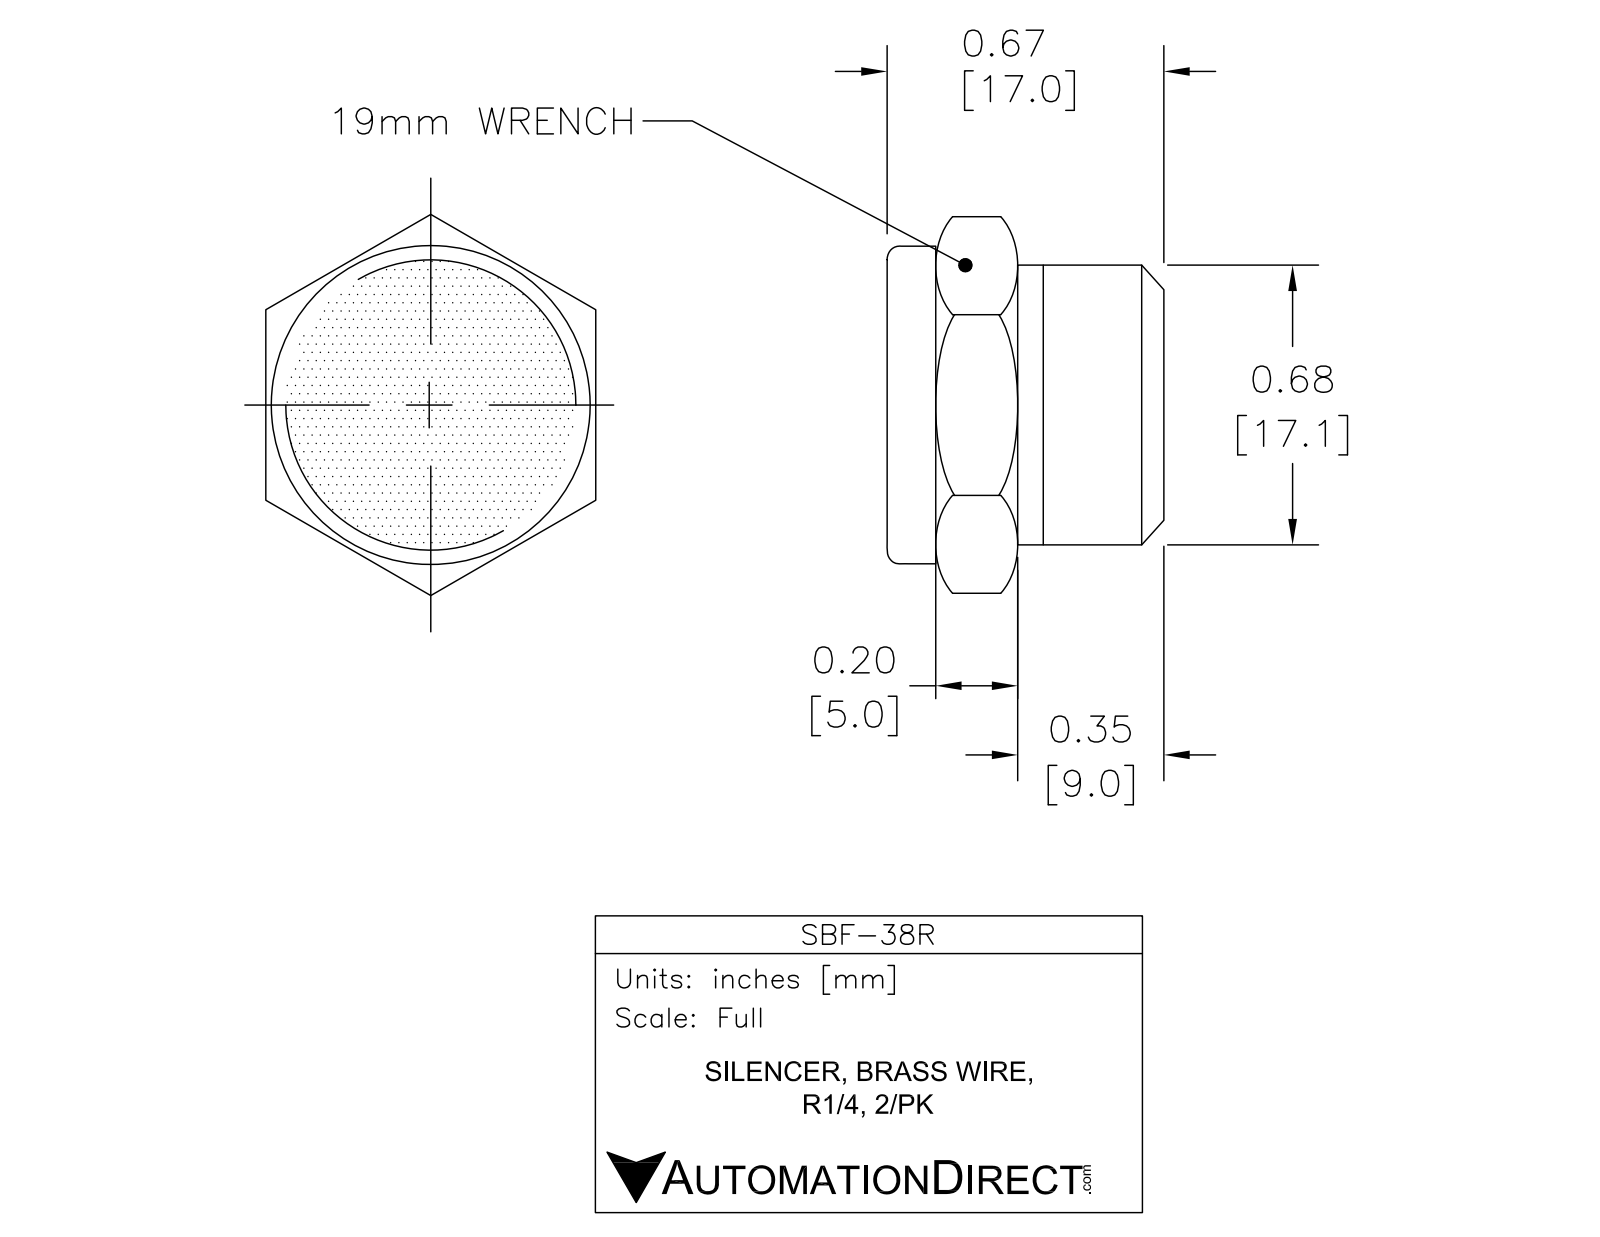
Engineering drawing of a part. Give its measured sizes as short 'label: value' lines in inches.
name: SBF-38R
written by: SolidWorks 2015 (CONFIG_CONTROL_DESIGN)
unit: in
bodies: 1 solid, 49 faces (12 planar, 17 cylindrical, 20 other)
size: 0.71 × 0.667 × 0.615
volume: 0.137 in³; area: 2.737 in²
holes: 1× ⌀0.314
bosses: 1× ⌀0.578
face distances: 0.615, 0.667, 0.5, 0.167, 0.32, 0.18, 0.347, 0.547, 0.227, 0.047
